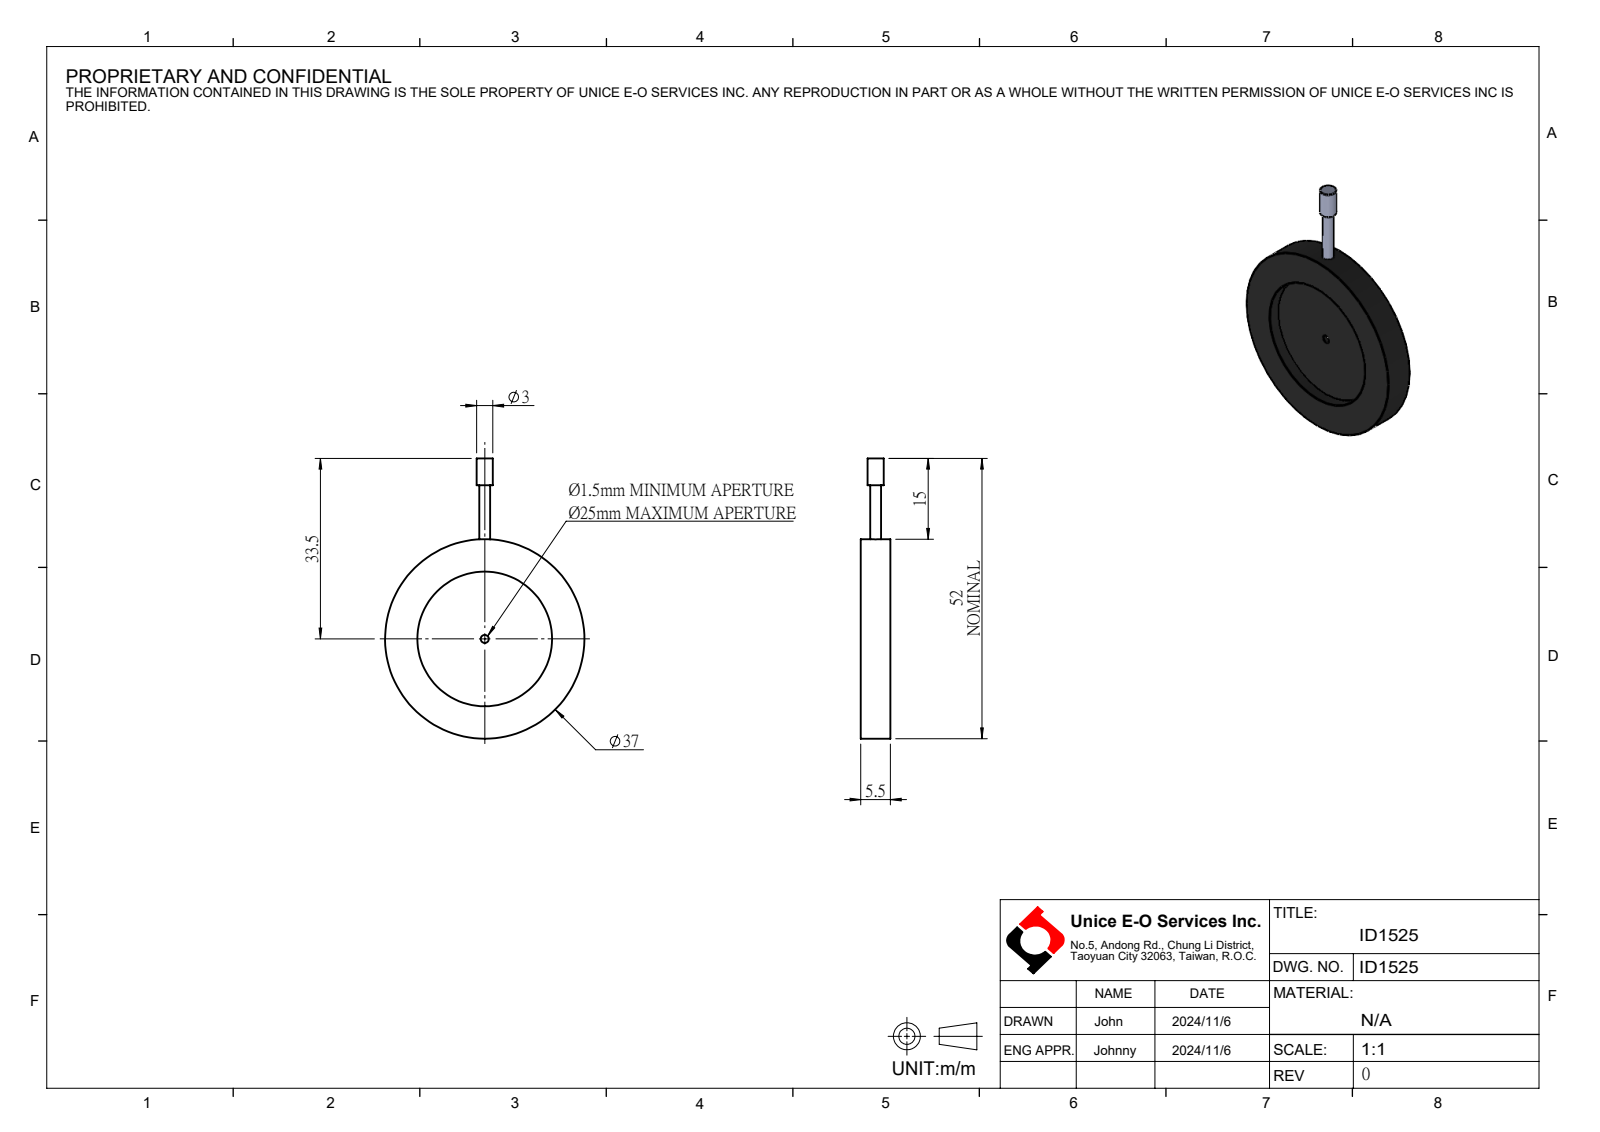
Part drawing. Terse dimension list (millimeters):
name: ID1525
written by: SolidWorks 2024 (AUTOMOTIVE_DESIGN)
unit: mm
bodies: 1 solid, 18 faces (6 planar, 12 cylindrical, 0 other)
size: 52 × 37 × 5.5
volume: 3 770 mm³; area: 3 262 mm²
holes: 1× ⌀1.5, 1× ⌀25
bosses: 1× ⌀37, 1× ⌀3, 1× ⌀2
face distances: 2.25, 3.25, 5.5, 1, 5
